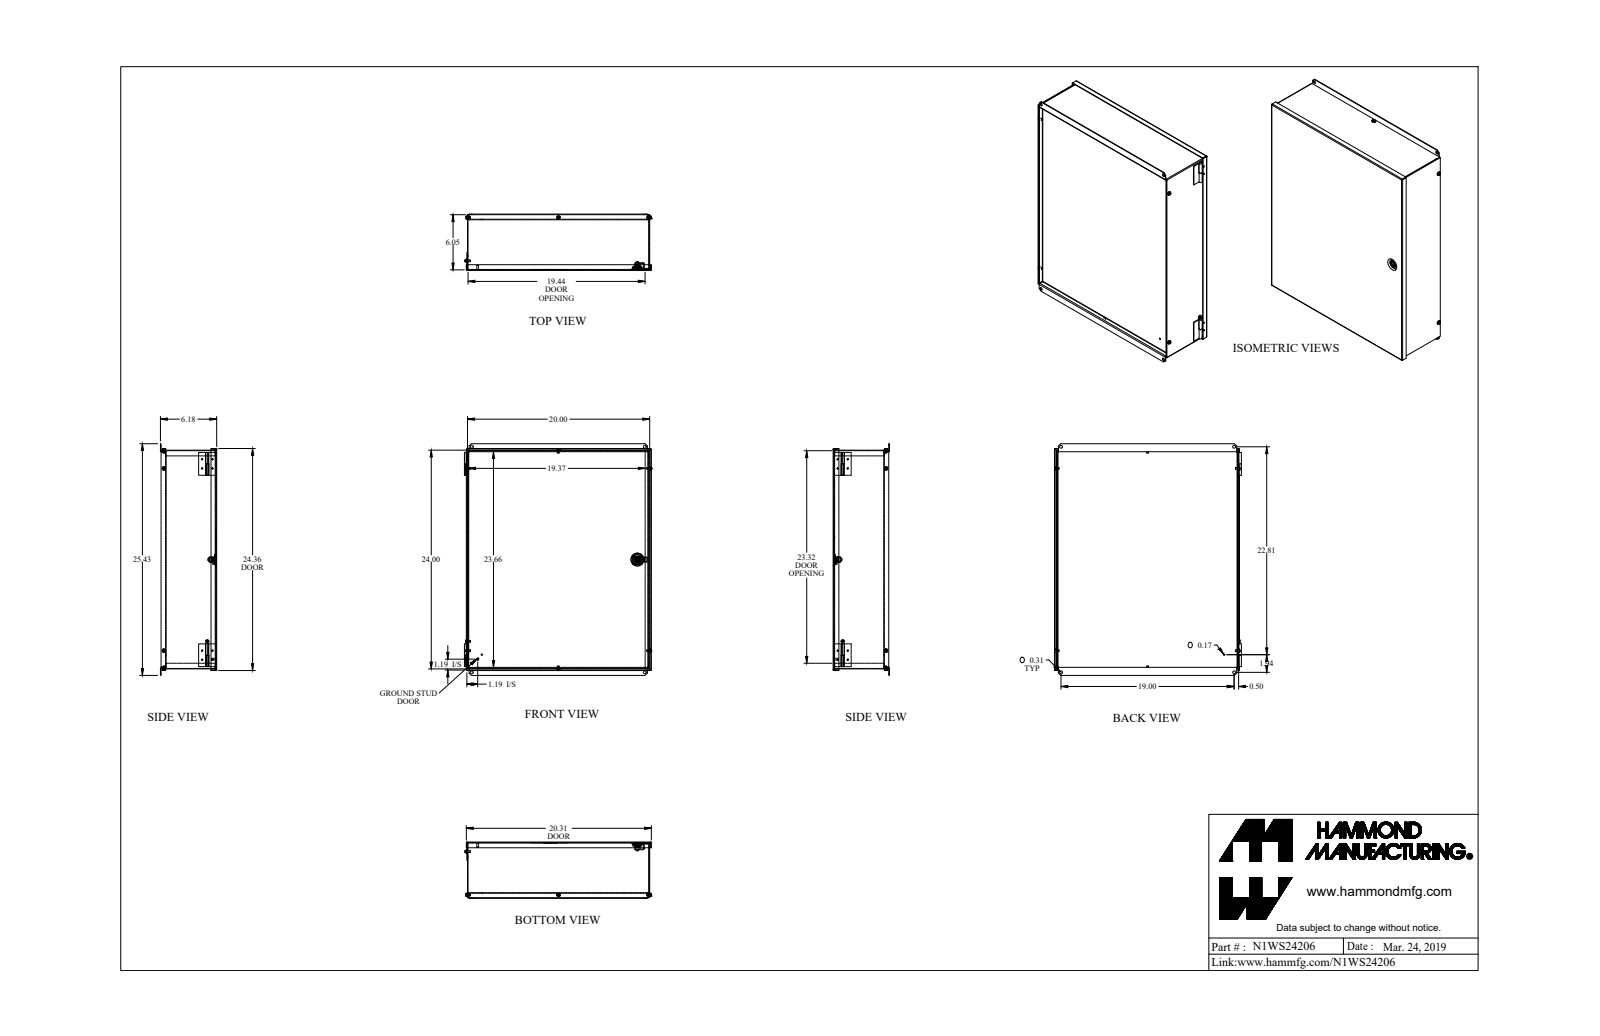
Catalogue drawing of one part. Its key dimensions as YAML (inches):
part_name: "N1WS24206"
step_written_by: "SolidWorks 2018 (AUTOMOTIVE_DESIGN)"
units: inches
bodies: {solids: 17, faces: 607, planar: 328, cylindrical: 214, other: 65}
overall_size: [25.425, 20.519, 6.179]
volume: 102.5
surface_area: 3320
round_holes:
  - {diameter: 0.14, count: 8}
  - {diameter: 0.17, count: 5}
  - {diameter: 0.312, count: 4}
  - {diameter: 0.187, count: 1}
  - {diameter: 0.319, count: 1}
  - {diameter: 0.476, count: 1}
round_bosses_or_shafts:
  - {diameter: 0.128, count: 8}
  - {diameter: 0.19, count: 4}
  - {diameter: 0.375, count: 3}
  - {diameter: 0.787, count: 1}
  - {diameter: 0.547, count: 1}
  - {diameter: 0.472, count: 1}
  - {diameter: 0.469, count: 1}
  - {diameter: 0.375, count: 1}
partial_cylinders:
  - {radius: 0.029, count: 9}
  - {radius: 0.086, count: 9}
  - {radius: 0.036, count: 8}
  - {radius: 0.108, count: 6}
  - {radius: 0.109, count: 6}
  - {radius: 0.012, count: 4}
  - {radius: 0.1, count: 4}
  - {radius: 0.079, count: 2}
face_to_face_distances: [0.057, 0.072, 0.057, 5.564, 5.621, 5.492, 5.549, 19.943, 23.943, 19.886]
hole_center_spacings: [1, 1.119, 1.501, 21, 21.03, 20, 4.195, 4.313]
